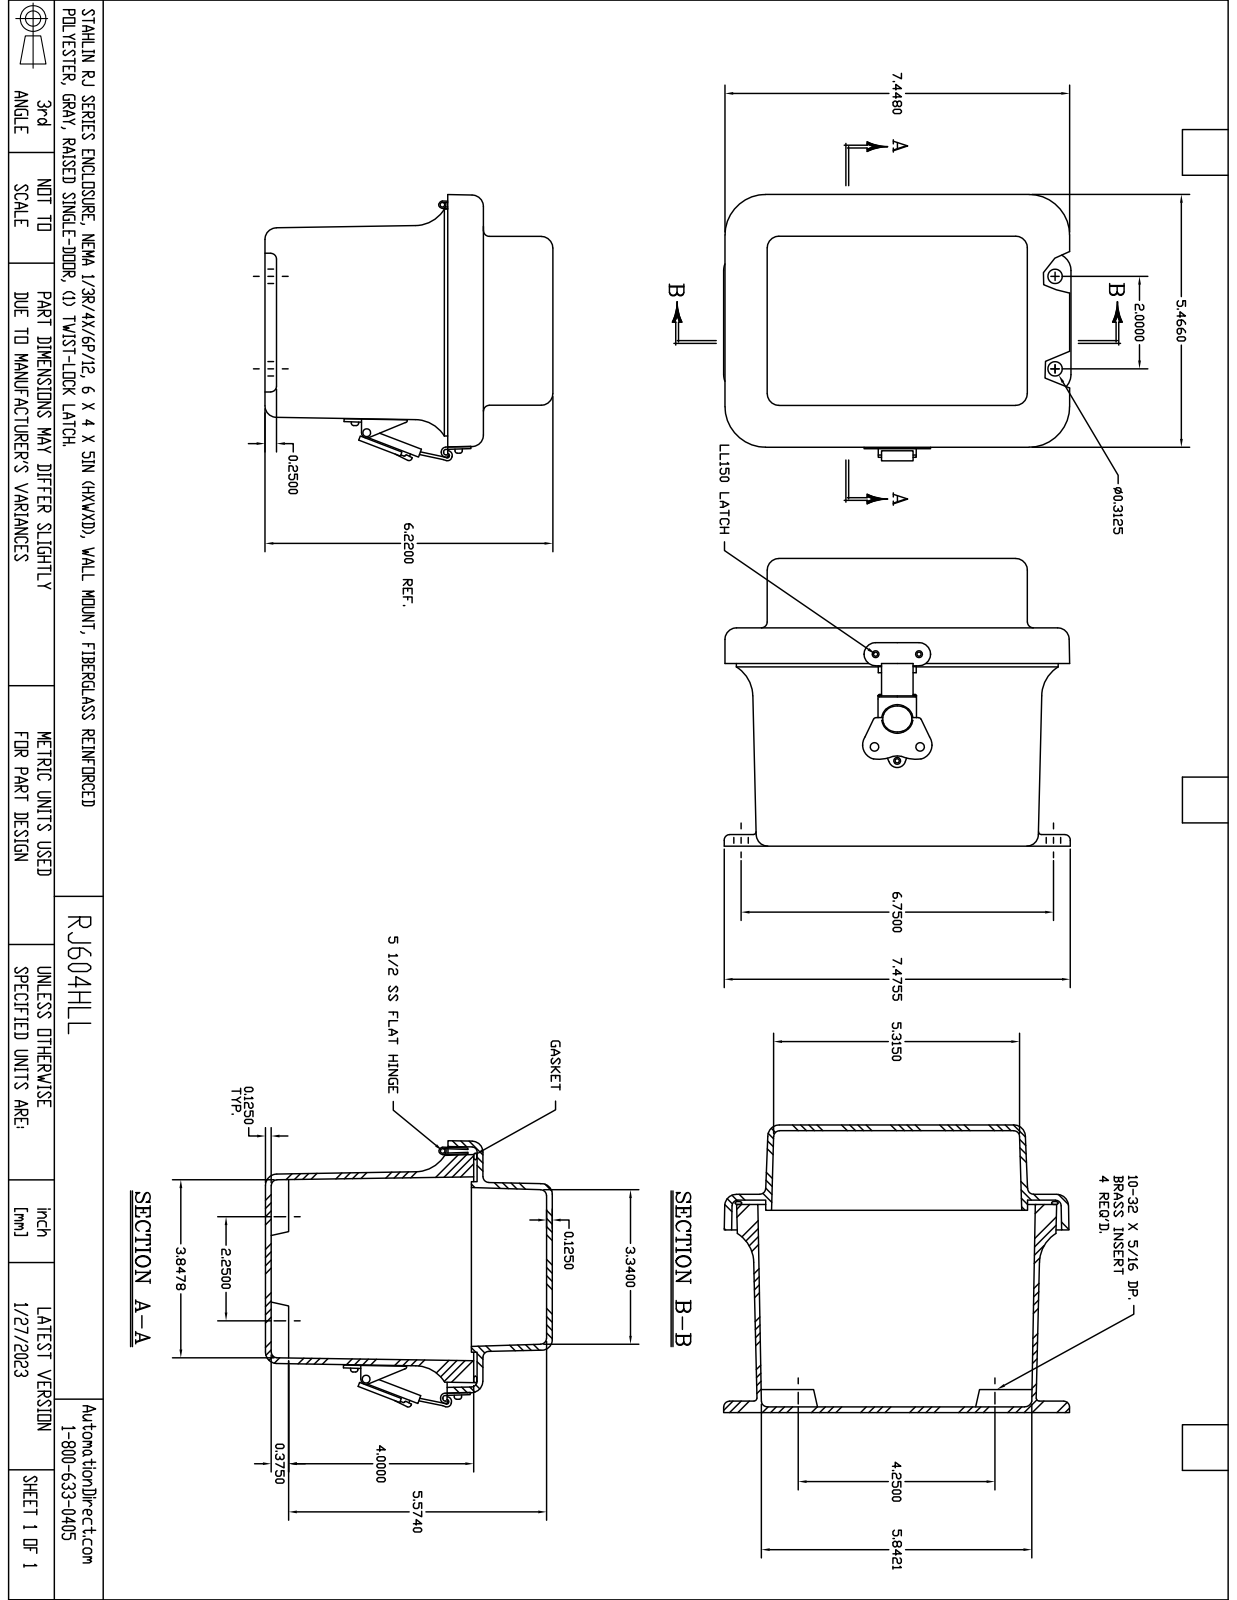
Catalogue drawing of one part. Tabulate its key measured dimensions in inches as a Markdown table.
| quantity | value |
| --- | --- |
| part name | MR604HLL |
| STEP written by | SolidWorks 2018 (AUTOMOTIVE_DESIGN) |
| units | inches |
| bodies | 30 solids, 775 faces (315 planar, 290 cylindrical, 170 other) |
| overall size | 7.474 × 6.227 × 5.674 |
| volume | 33.66 in³ |
| surface area | 459.5 in² |
| round holes (diameter × count) | 0.14 × 9, 0.131 × 5, 0.152 × 5, 0.156 × 4, 0.218 × 4, 0.13 × 2, 0.165 × 2, 0.197 × 2, 0.085 × 1, 0.106 × 1, 0.118 × 1, 0.138 × 1 |
| round bosses / shafts (diameter × count) | 0.25 × 9, 0.125 × 5, 0.27 × 4, 0.125 × 4, 0.583 × 1, 0.524 × 1, 0.209 × 1, 0.185 × 1 |
| partial cylindrical surfaces (radius × count) | 0.031 × 20, 0.125 × 20, 0.25 × 12, 0.079 × 10, 0.037 × 4, 0.039 × 4, 0.045 × 4, 0.047 × 4 |
| main face-to-face distances | 0.125, 4.602, 6.102, 1.5, 6.227, 1.625, 4.477, 5.977, 0.774, 4.727 |
| hole center spacings | 2.5, 3.339, 0.276, 0.469, 0.5, 0.826, 0.826, 0.938 |
